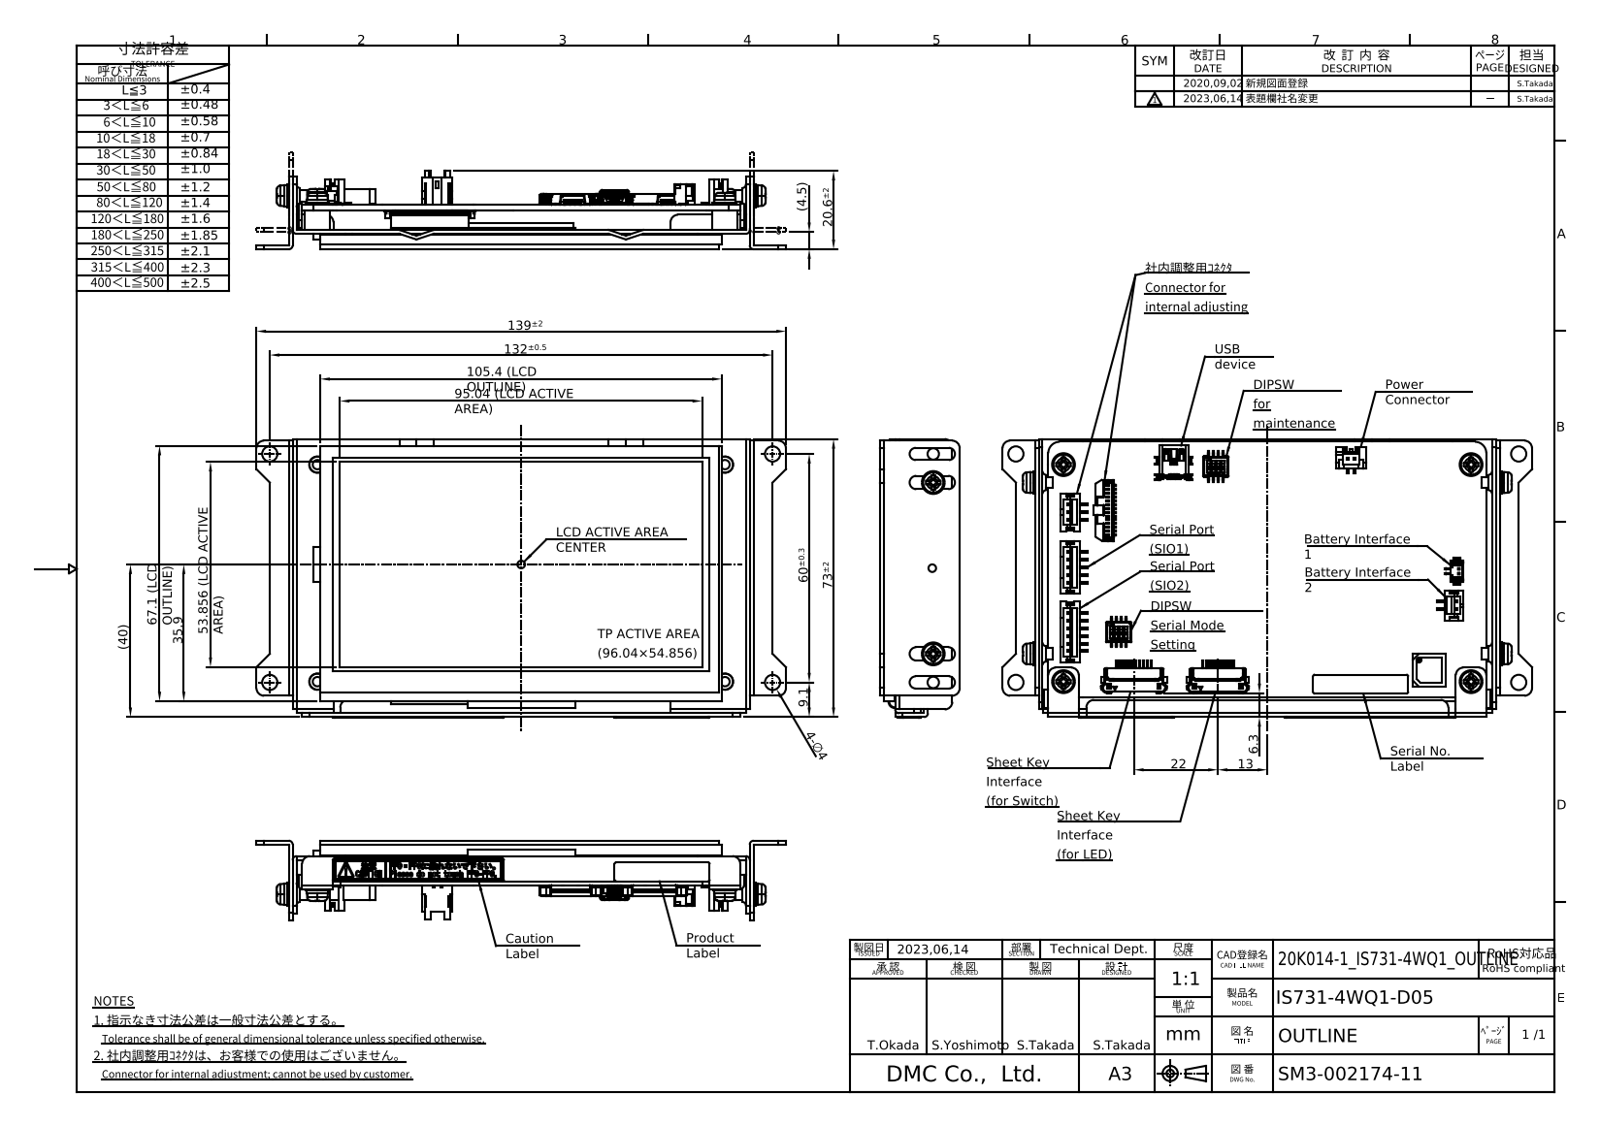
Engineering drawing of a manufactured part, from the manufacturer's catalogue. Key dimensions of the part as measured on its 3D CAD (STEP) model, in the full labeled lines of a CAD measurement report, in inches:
Part name (STEP PRODUCT): HP_IS731-4WQ1-D05
STEP written by: Autodesk Inventor 2017 (AUTOMOTIVE_DESIGN)
Units: inches
Bodies: 1 solid, 5561 faces (4115 planar, 809 cylindrical, 637 other)
Overall size (bounding box): 5.472 × 2.882 × 0.827
Volume: 3.697 in³ · Surface area: 90.3 in²
Round holes (diameter × count): ⌀0.157 ×6, ⌀0.097 ×4, ⌀0.138 ×4, ⌀0.167 ×4, ⌀0.039 ×2, ⌀0.047 ×2, ⌀0.012 ×1, ⌀0.052 ×1, ⌀0.079 ×1
Round bosses / shafts (diameter × count): ⌀0.118 ×8, ⌀0.236 ×6, ⌀0.217 ×6, ⌀0.315 ×4, ⌀0.256 ×4, ⌀0.167 ×4
Partial cylindrical surfaces — rounded edges, fillets, slot ends (radius × count): R0.004 ×116, R0.008 ×50, R0.012 ×48, R0.006 ×29, R0.079 ×20, R0.005 ×16, R0.016 ×15, R0.02 ×13
Main face-to-face distances: 0.26, 0.459, 0.199, 0.063, 0.039, 0.197, 0.396, 0.16, 0.236, 0.299
Hole centre spacings: 0.492, 0.504, 2.244, 2.305, 2.362, 2.405, 2.726, 4.213
